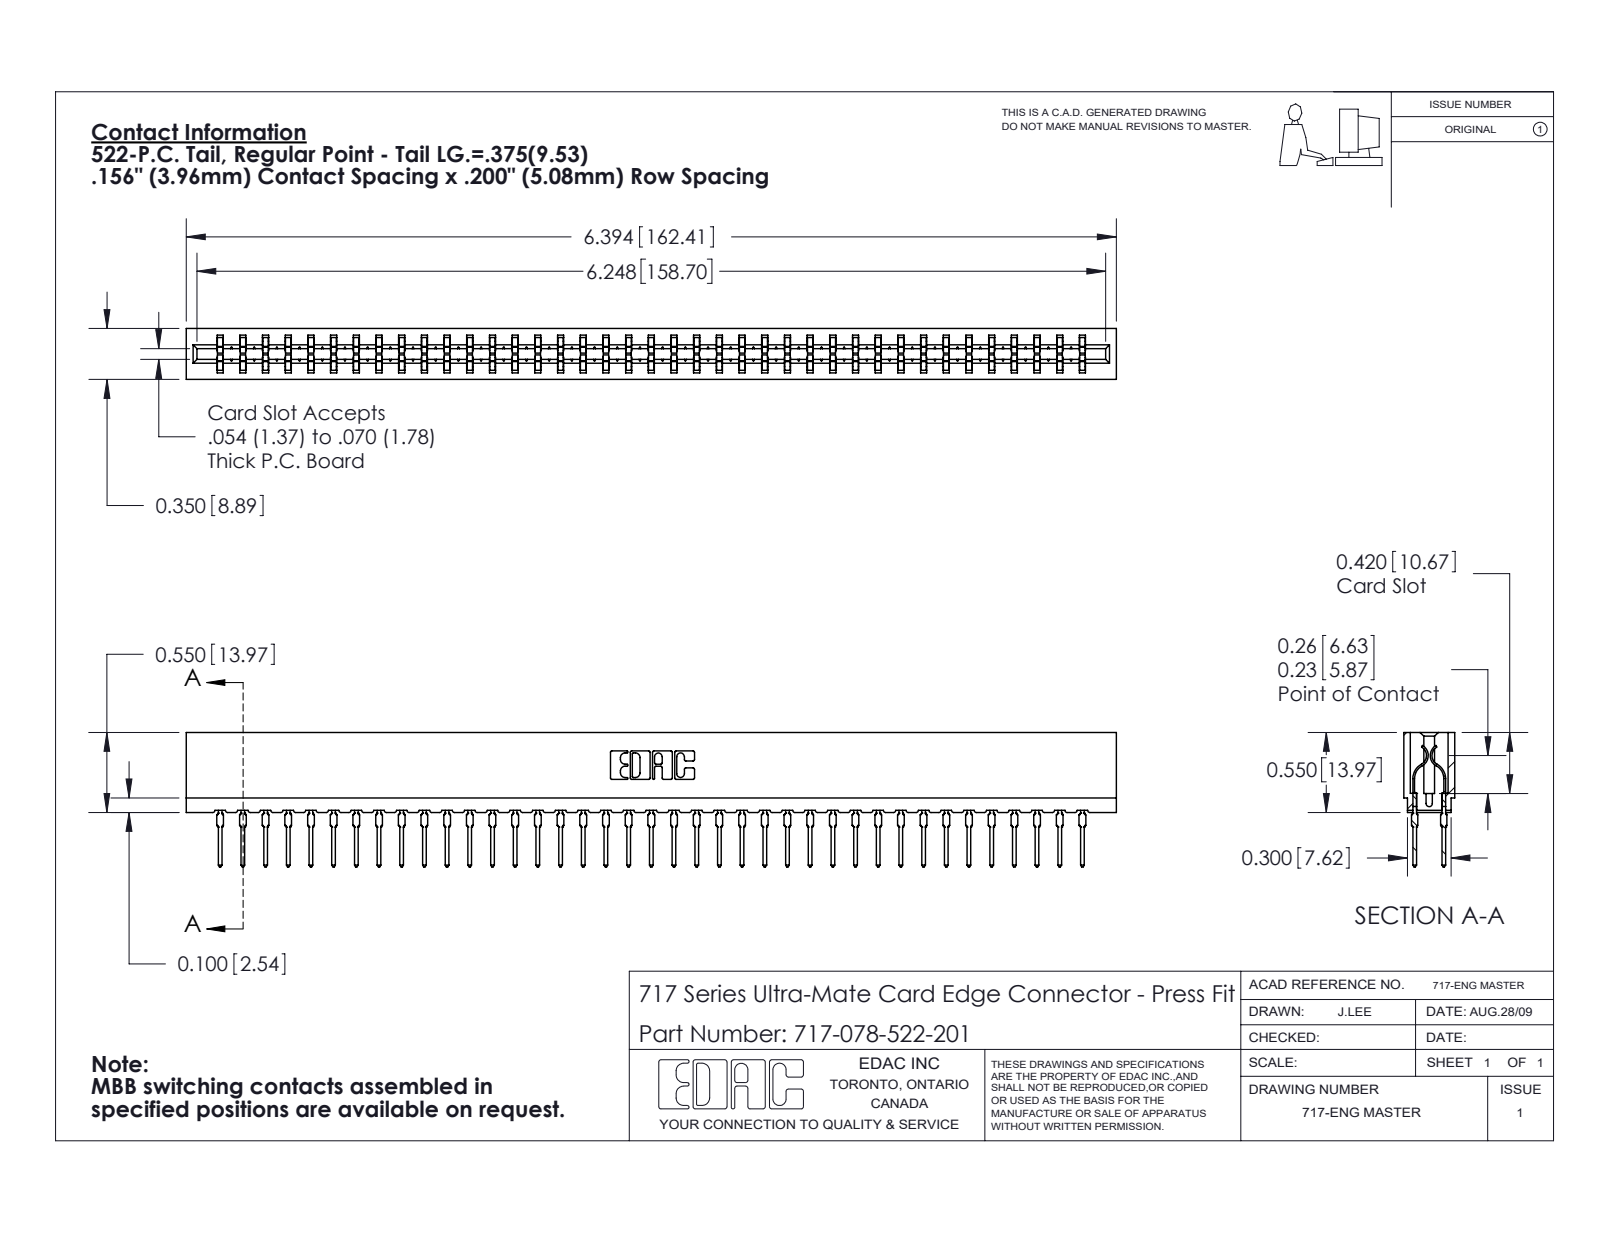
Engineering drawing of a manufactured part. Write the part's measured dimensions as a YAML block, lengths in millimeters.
part_name: "745-292-001_522; 717 Part_Insulator Option - 06; 717-078-522-201"
step_written_by: "SolidWorks 2020 (CONFIG_CONTROL_DESIGN)"
units: millimeters
bodies: {solids: 79, faces: 7114, planar: 3681, cylindrical: 1405, other: 2028}
overall_size: [162.4, 23.5, 8.9]
volume: 14200
surface_area: 21940
partial_cylinders:
  - {radius: 0.5, count: 156}
  - {radius: 0.4, count: 78}
  - {radius: 0.3, count: 22}
  - {radius: 0.1, count: 8}
  - {radius: 0.3, count: 8}
  - {radius: 0.2, count: 6}
  - {radius: 0.8, count: 6}
  - {radius: 0.7, count: 3}
face_to_face_distances: [5.4, 3.5, 8.9, 1.6, 7.3, 1.9, 3.8, 1.9, 1.1, 7.7]
